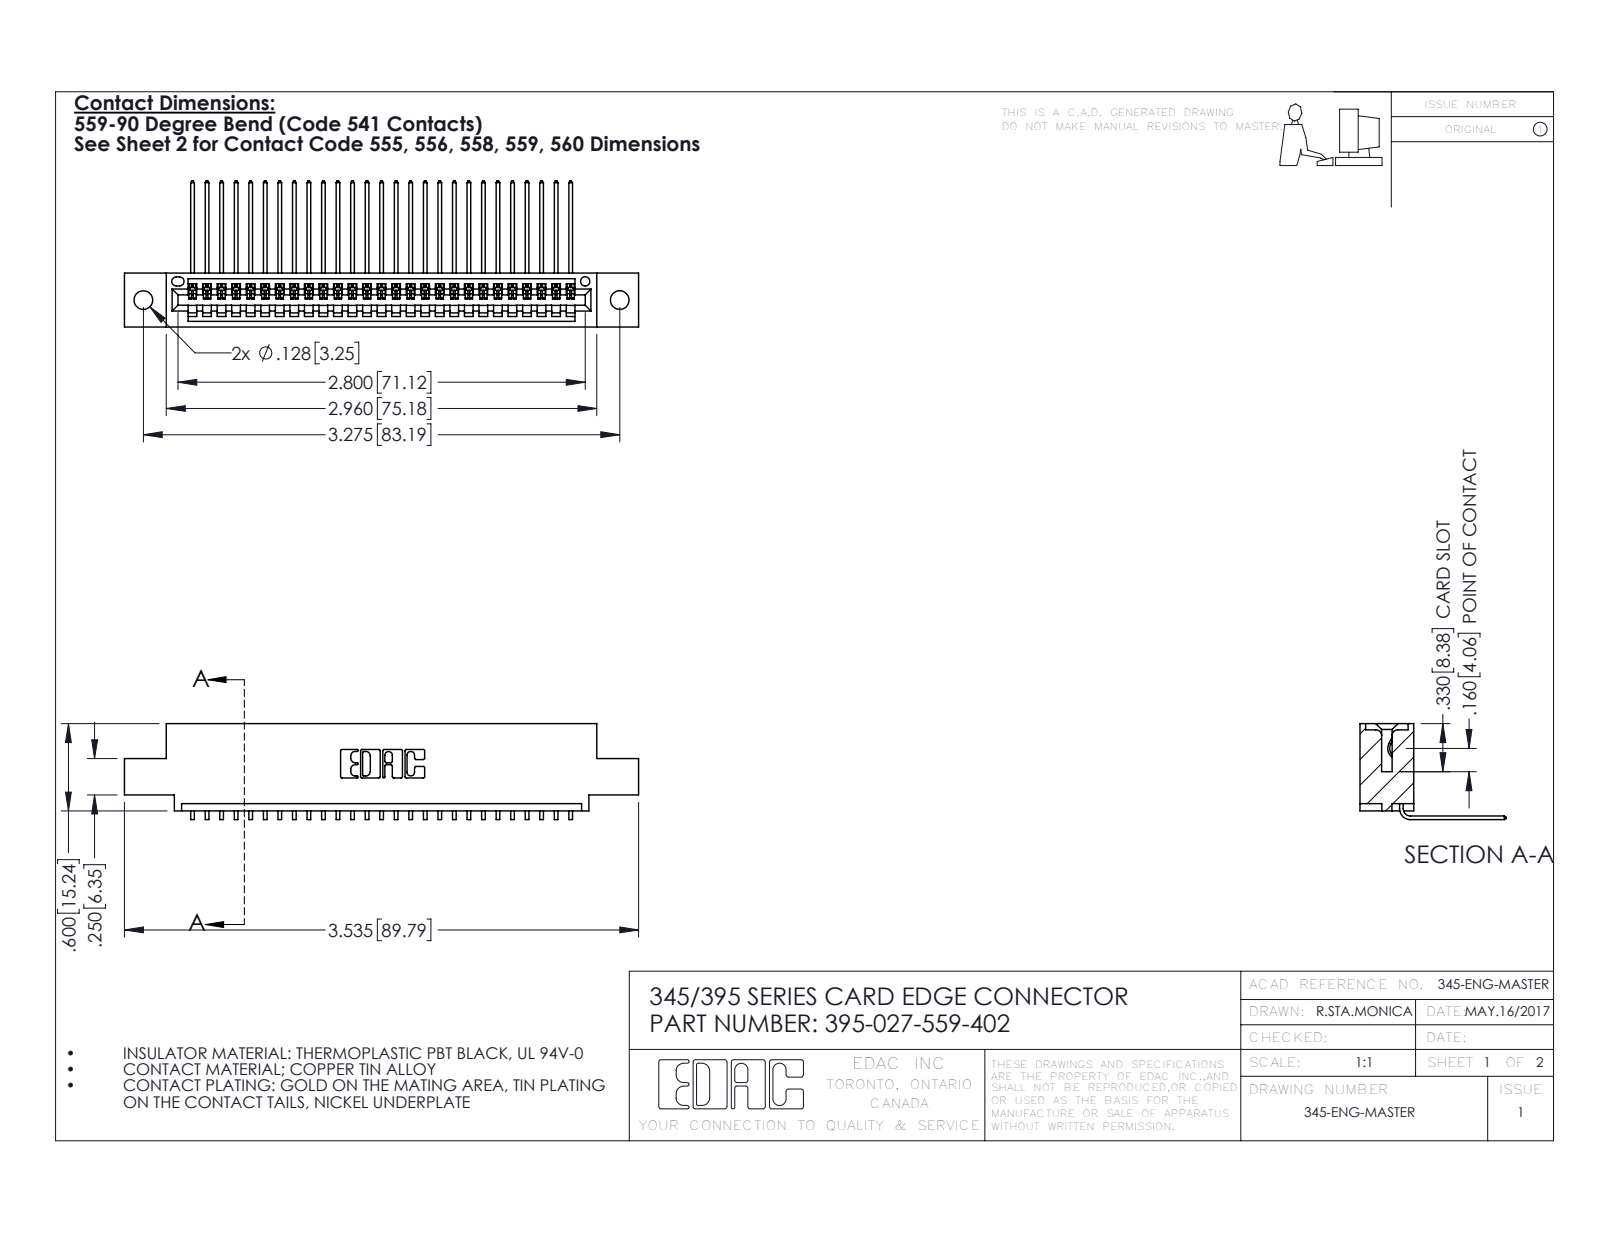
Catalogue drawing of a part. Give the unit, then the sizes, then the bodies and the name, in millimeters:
Units: millimetres
Overall size (bounding box): 89.8 × 25.5 × 16.7
Round holes (diameter × count): ⌀3.3 ×2, ⌀1.6 ×1
Partial cylindrical surfaces — rounded edges, fillets, slot ends (radius × count): R0.2 ×54, R0.3 ×22, R0.2 ×6, R0.8 ×6, R0.7 ×3, R0.8 ×2, R1 ×2, R0.4 ×1
Main face-to-face distances: 1.8, 7.6, 9.4, 5.1, 2.5, 6.9, 0.6, 5.7, 3.8, 1.8
Hole centre spacings: 6.9, 77.2, 83.2
Volume: 8 390 mm³ · Surface area: 11 280 mm²
Bodies: 28 solids, 1750 faces (1218 planar, 532 cylindrical, 0 other)
Part name (STEP PRODUCT): 395-027-559-402; 345-292-001_558 559 Tail - 1; 345 Part_0.110 Offset - 0.128 Dia
STEP written by: SolidWorks 2016 (CONFIG_CONTROL_DESIGN)
